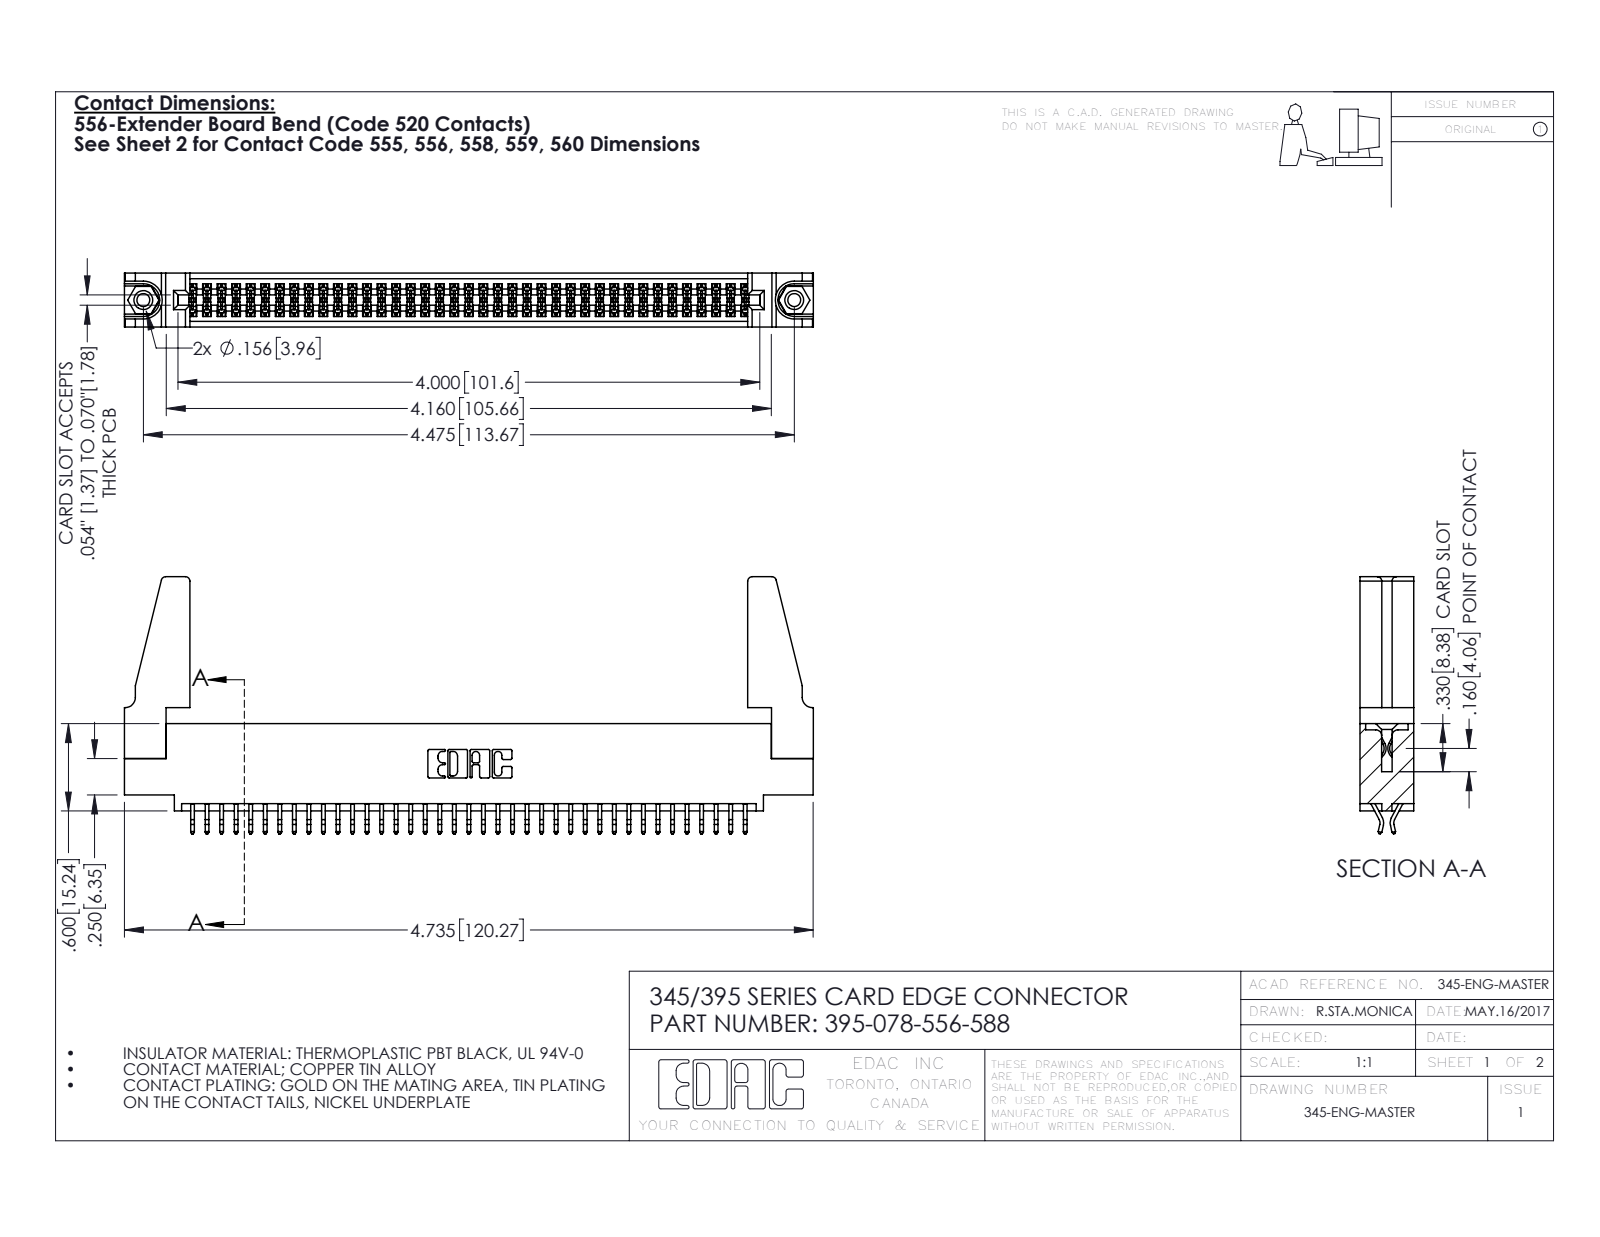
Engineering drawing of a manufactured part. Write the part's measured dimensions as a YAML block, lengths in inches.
part_name: "345-292-001_556 Tail; 345-220-078_345-220-088; 395-078-556-588; 345-250-001_345-250-001-102 (+1 more)"
step_written_by: "SolidWorks 2016 (CONFIG_CONTROL_DESIGN)"
units: inches
bodies: {solids: 83, faces: 4622, planar: 3042, cylindrical: 1564, other: 16}
overall_size: [4.736, 1.767, 0.37]
volume: 0.905
surface_area: 31.32
round_holes:
  - {diameter: 0.089, count: 2}
  - {diameter: 0.125, count: 2}
  - {diameter: 0.156, count: 2}
  - {diameter: 0.064, count: 1}
round_bosses_or_shafts:
  - {diameter: 0.155, count: 2}
partial_cylinders:
  - {radius: 0.006, count: 117}
  - {radius: 0.01, count: 22}
  - {radius: 0.03, count: 8}
  - {radius: 0.007, count: 6}
  - {radius: 0.031, count: 6}
  - {radius: 0.026, count: 3}
  - {radius: 0.01, count: 2}
  - {radius: 0.014, count: 2}
face_to_face_distances: [0.072, 0.298, 0.37, 0.025, 0.2, 0.098, 0.272, 0.225, 0.175, 0.149]
hole_center_spacings: [0.27, 4.239, 4.475]
